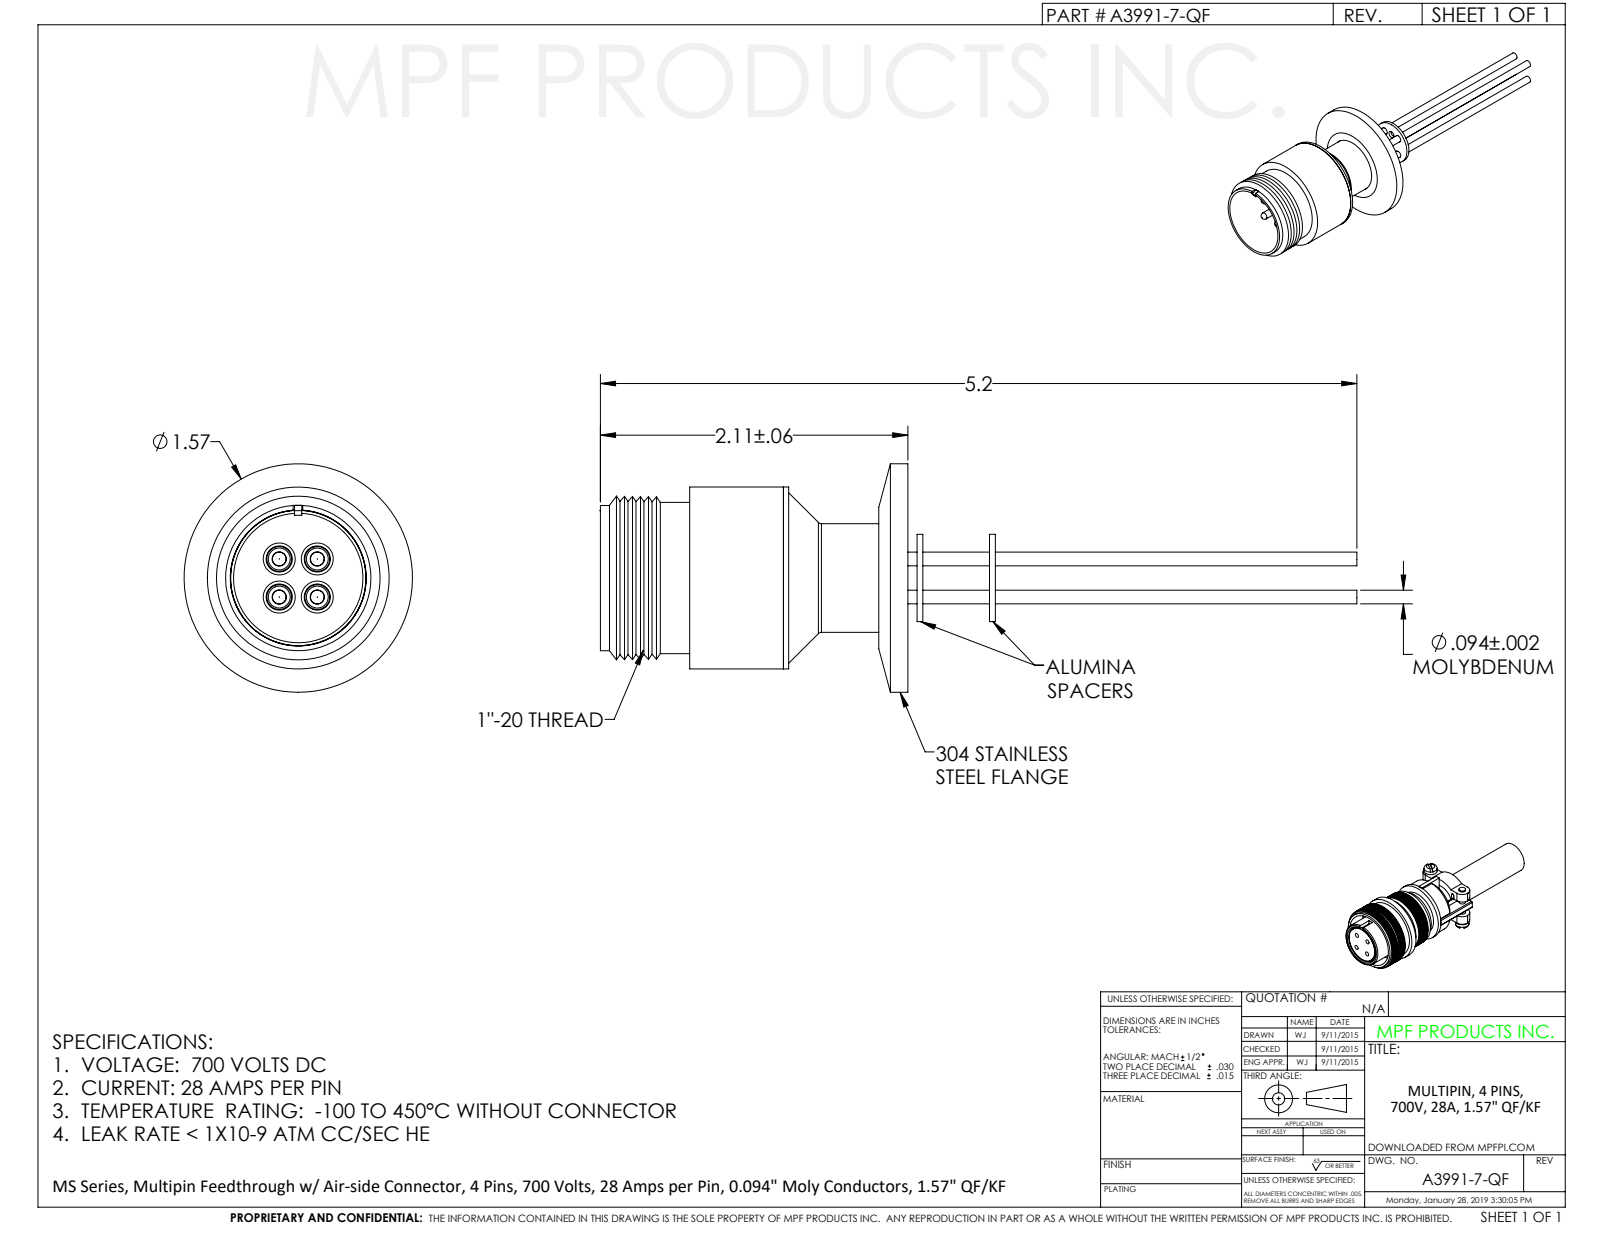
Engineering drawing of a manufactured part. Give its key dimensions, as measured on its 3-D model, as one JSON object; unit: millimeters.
{"part_name": "A3991-7-QF", "step_written_by": "SolidWorks 2012 (CONFIG_CONTROL_DESIGN)", "units": "millimeters", "bodies": {"solids": 1, "faces": 166, "planar": 35, "cylindrical": 85, "other": 46}, "overall_size": [132.2, 39.9, 39.9], "volume_mm3": 16730, "surface_area_mm2": 18430, "round_holes": [[2.5, 2], [17.1, 1], [23.7, 1], [23.7, 1], [24.9, 1], [26.5, 1], [29.5, 1]], "round_bosses_or_shafts": [[5.2, 4], [4.6, 4], [2.4, 4], [39.9, 1], [31.8, 1], [26.9, 1], [26.4, 1], [25.4, 1]], "face_to_face_distances": [34.2, 4.1, 30.1, 31.7, 27.6, 2.5, 3.7, 7.8, 35.4, 37.9], "hole_center_spacings": [3.4, 6.9]}
